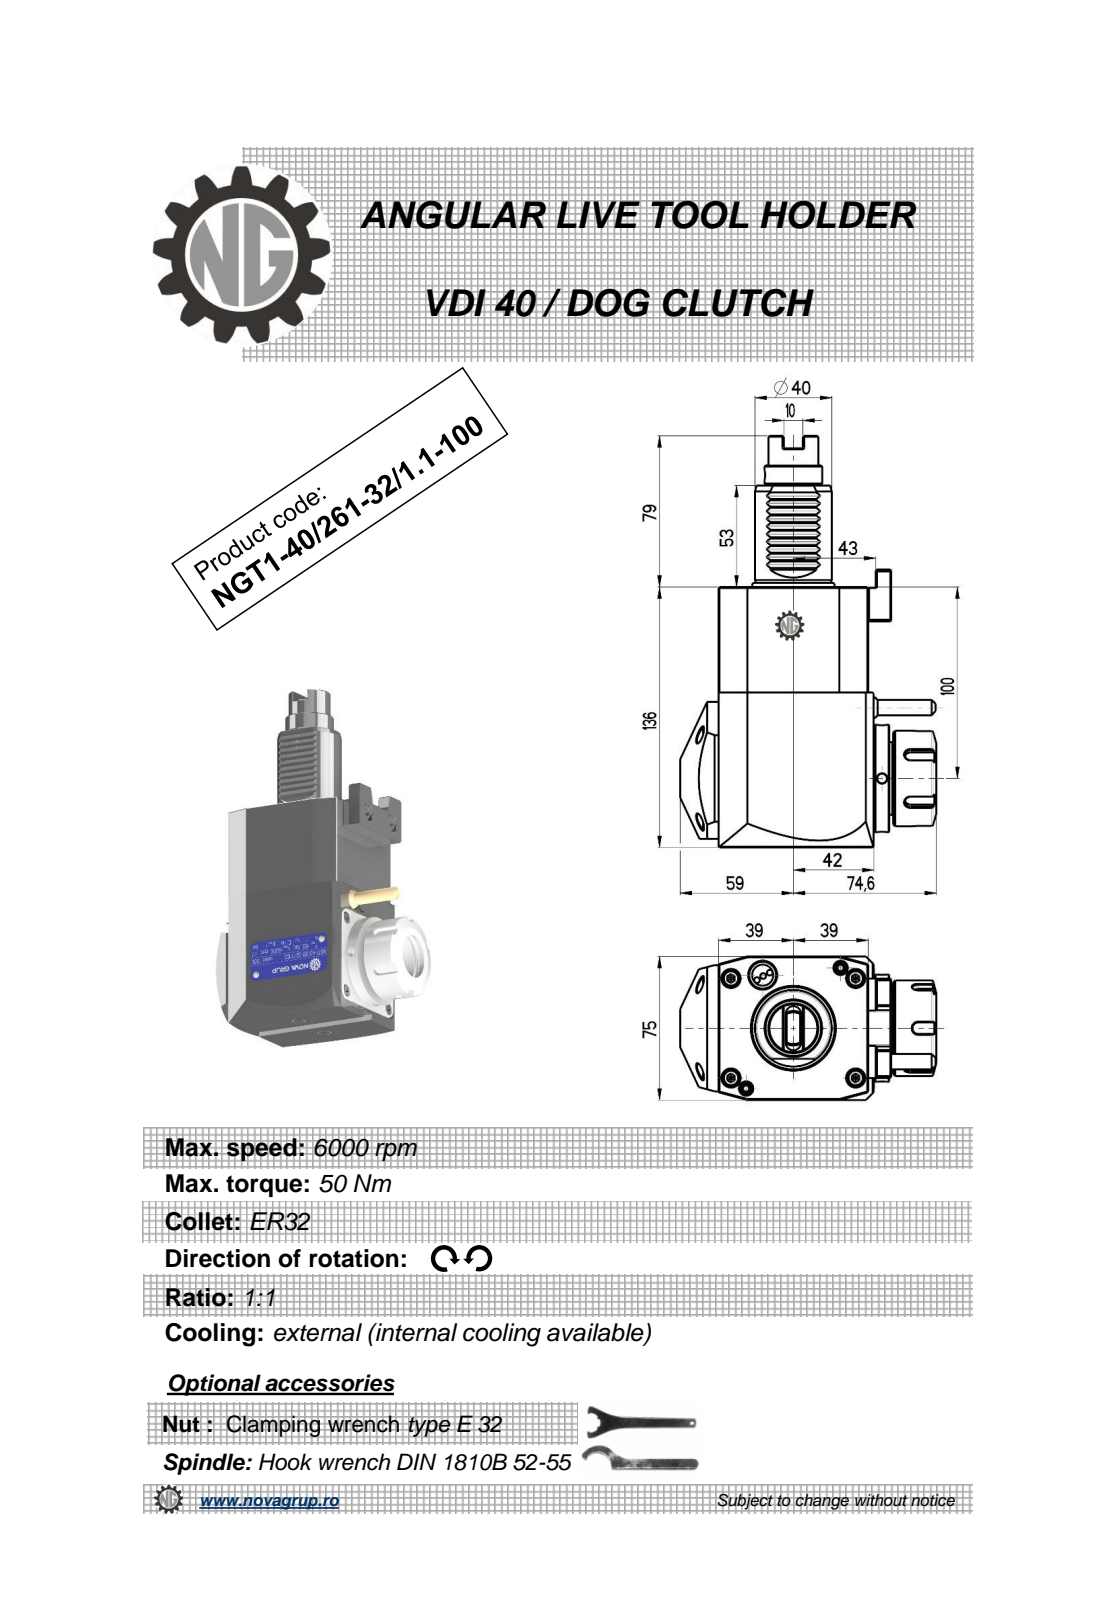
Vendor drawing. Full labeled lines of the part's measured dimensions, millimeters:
Part name (STEP PRODUCT): NGT1_40_261_32_1_1_100
STEP written by: PRO/ENGINEER BY PARAMETRIC TECHNOLOGY CORPORATION, 2010280 (CONFIG_CONTROL_DESIGN)
Units: millimetres
Bodies: 1 solid, 388 faces (199 planar, 74 cylindrical, 115 other)
Overall size (bounding box): 215 × 133.6 × 75
Volume: 1 003 000 mm³ · Surface area: 77 508 mm²
Round holes (diameter × count): ⌀5 ×3, ⌀3 ×1, ⌀4.2 ×1, ⌀27 ×1
Round bosses / shafts (diameter × count): ⌀56 ×1, ⌀50 ×1, ⌀43 ×1, ⌀41 ×1, ⌀40 ×1, ⌀30 ×1, ⌀26 ×1, ⌀11.2 ×1
Partial cylindrical surfaces — rounded edges, fillets, slot ends (radius × count): R0.3 ×10, R0.22 ×6, R0.26 ×6, R3 ×5, R0.5 ×3, R1 ×2, R12.5 ×1, R40 ×1
Main face-to-face distances: 75, 136, 78, 81, 3, 0.5, 84.88, 1, 80.8, 2.8
Hole centre spacings: 40.93, 122.75, 158.5
